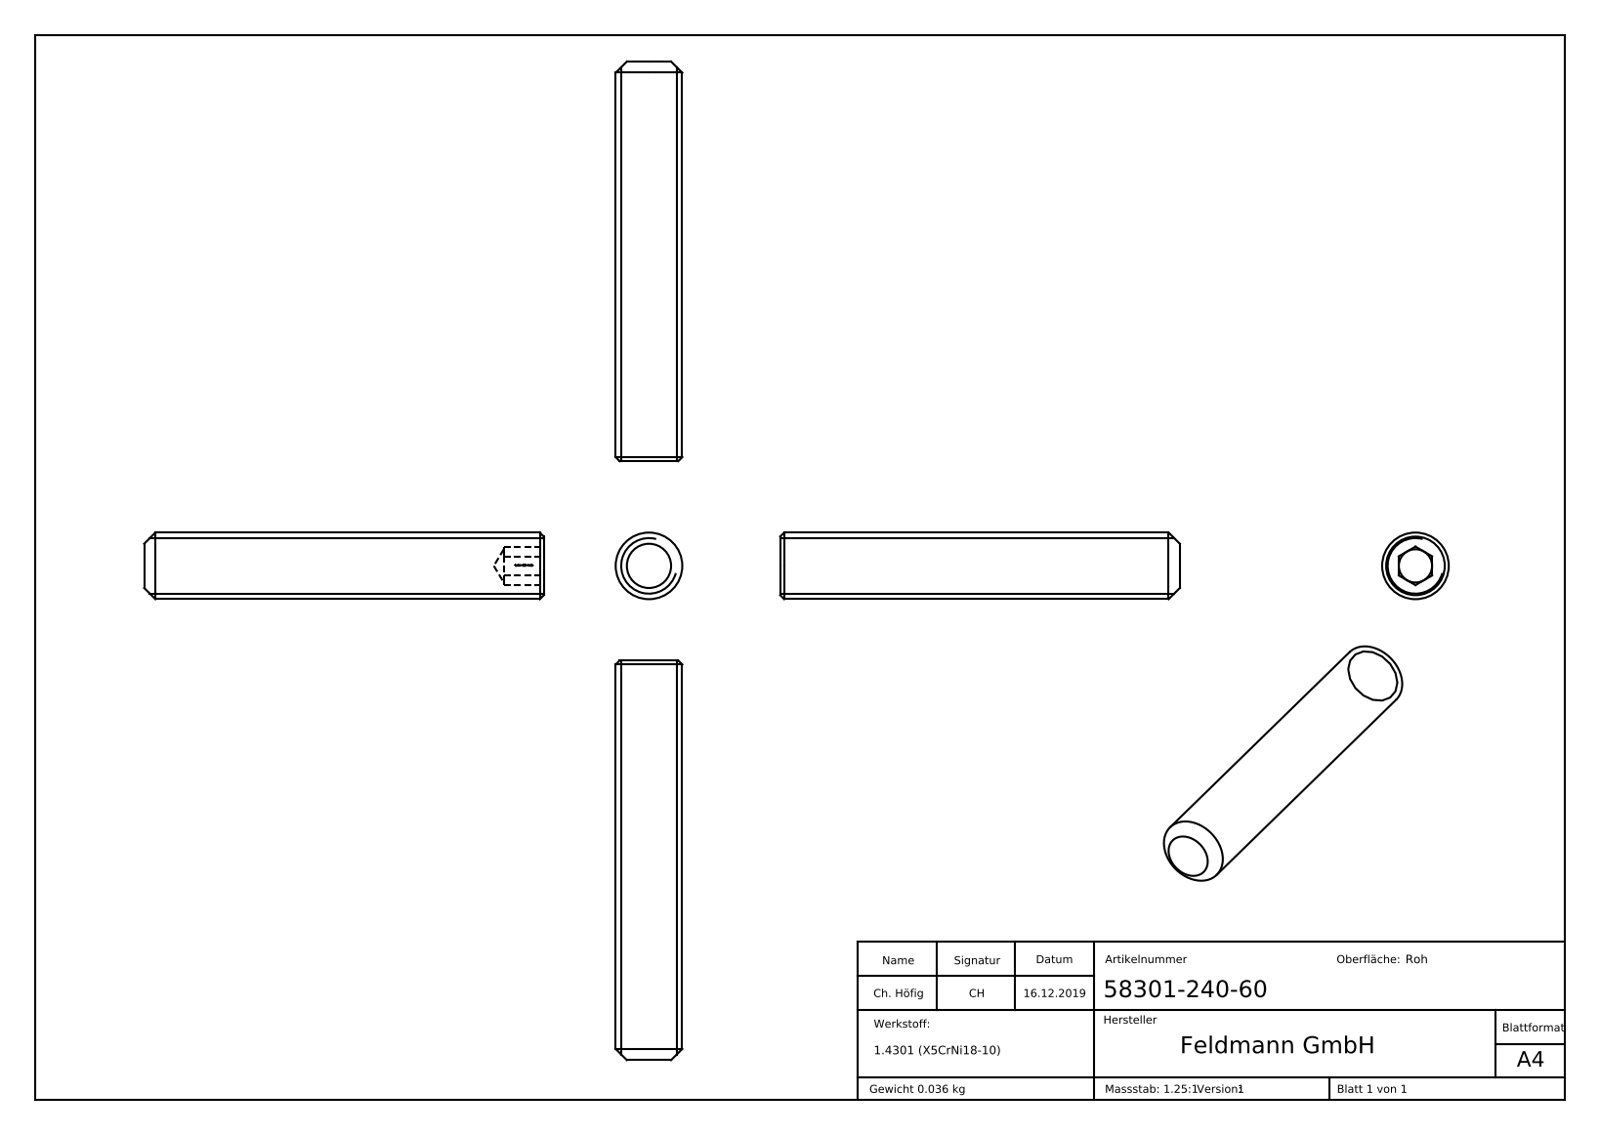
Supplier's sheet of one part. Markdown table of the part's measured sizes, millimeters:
| quantity | value |
| --- | --- |
| part name | 58301-240-60 |
| STEP written by | SolidWorks 2015 (CONFIG_CONTROL_DESIGN) |
| units | millimeters |
| bodies | 1 solid, 293 faces (139 planar, 1 cylindrical, 153 other) |
| overall size | 110 × 10 × 10 |
| volume | 4 528 mm³ |
| surface area | 2 105 mm² |
| round bosses / shafts (diameter × count) | 10 × 1 |
| main face-to-face distances | 5, 60, 54, 6, 5.1, 0.37, 0.48, 0.54, 0.82, 0.96 |
